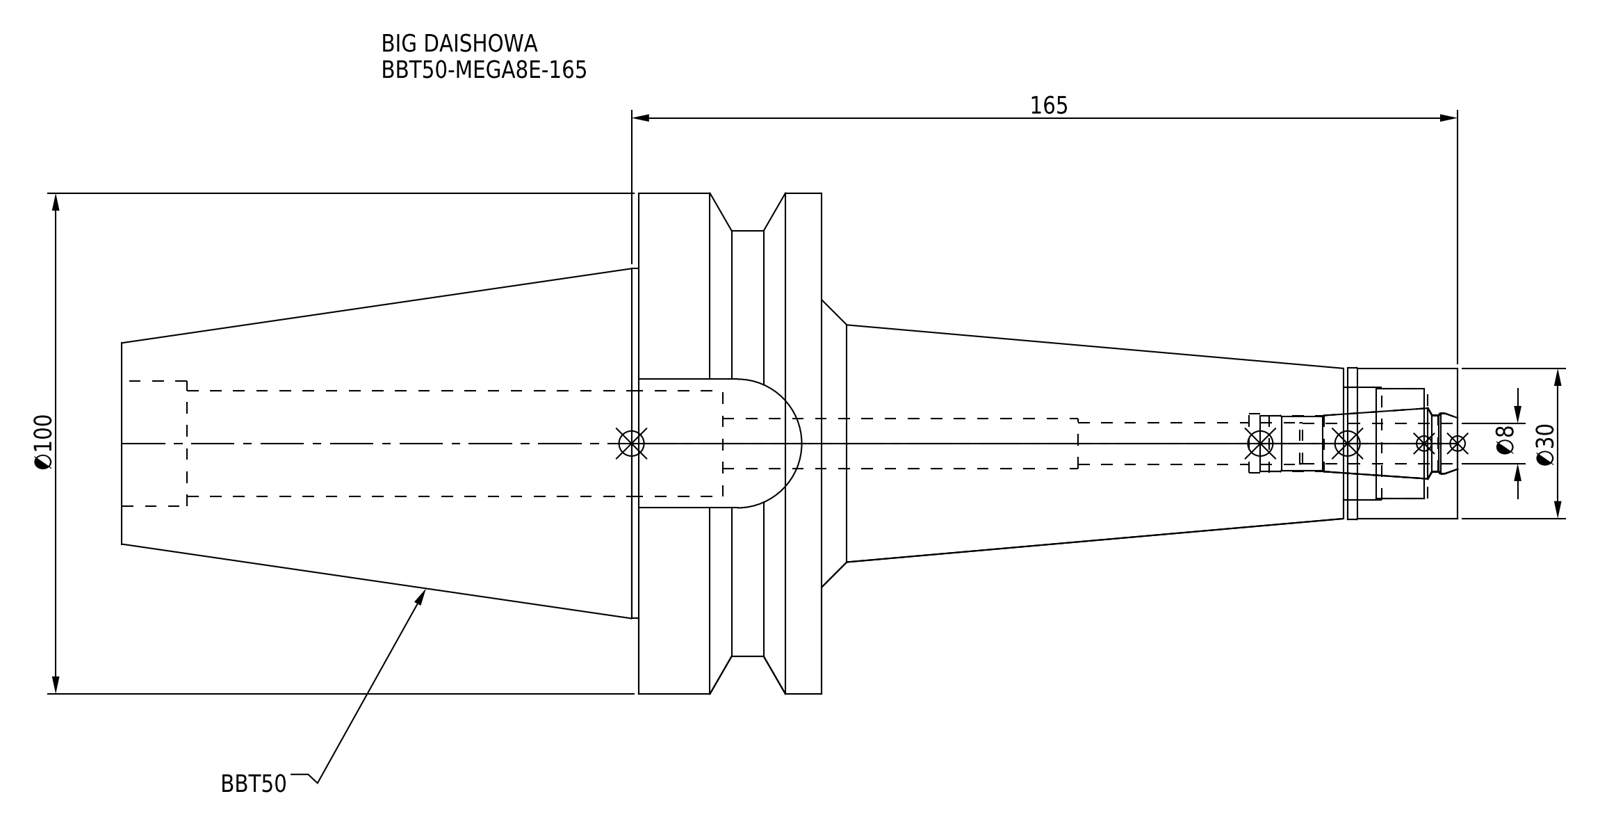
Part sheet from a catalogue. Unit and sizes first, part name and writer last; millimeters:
Units: millimetres
Overall size (bounding box): 266.8 × 100 × 100
Round holes (diameter × count): ⌀8.4 ×1, ⌀10 ×1, ⌀11.2 ×1, ⌀11.4 ×1, ⌀11.8 ×1, ⌀12.3 ×1, ⌀21.2 ×1, ⌀22 ×1, ⌀22.5 ×1, ⌀25 ×1
Round bosses / shafts (diameter × count): ⌀100 ×1, ⌀85 ×1, ⌀69.85 ×1, ⌀30.3 ×1, ⌀30 ×1
Partial cylindrical surfaces — rounded edges, fillets, slot ends (radius × count): R12.85 ×1
Main face-to-face distances: 36.5, 139.8, 103.3, 70.8, 127, 163.5, 266.8, 25.7, 22, 105
Volume: 587 620 mm³ · Surface area: 74 975 mm²
Bodies: 2 solids, 81 faces (21 planar, 40 cylindrical, 20 other)
Part name (STEP PRODUCT): BBT50-MEGA8E-165-080.stp; BBT50-MEGA8E-165; MEN8_1.stp; DXF_TEMP_ASSY_ASM_4_ASM.stp (+3 more)
STEP written by: SolidWorks 2019 (CONFIG_CONTROL_DESIGN)
